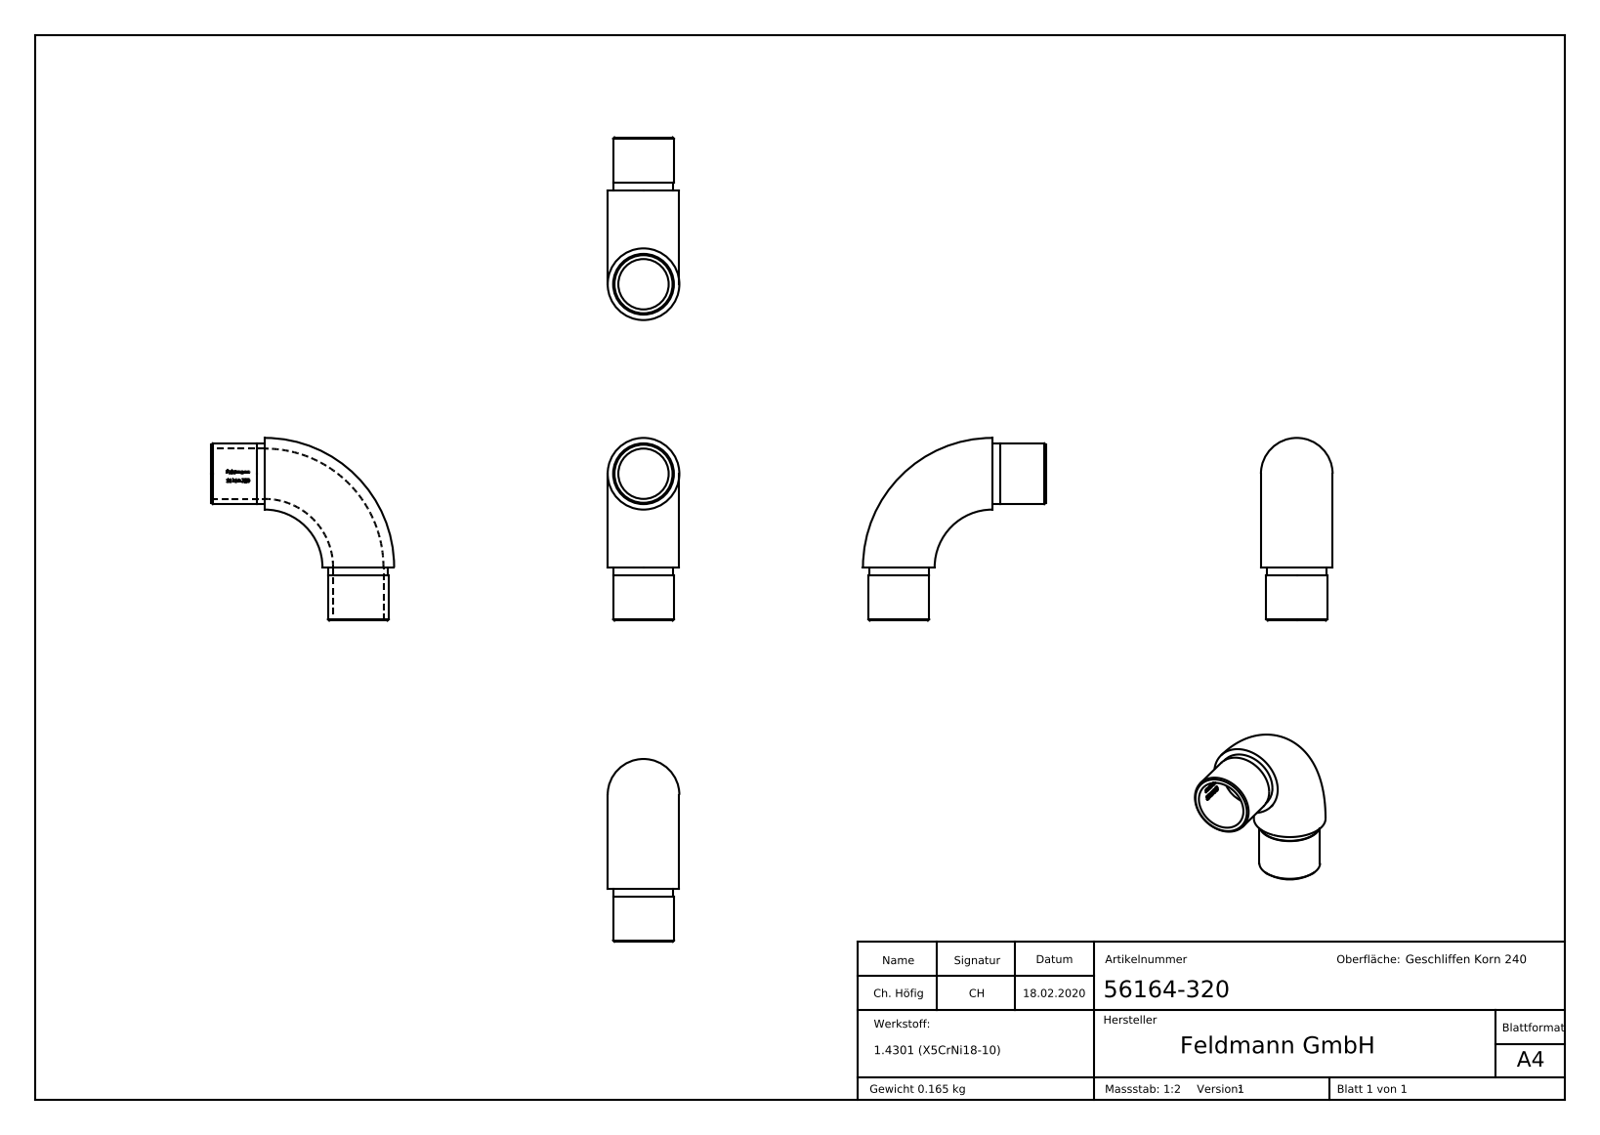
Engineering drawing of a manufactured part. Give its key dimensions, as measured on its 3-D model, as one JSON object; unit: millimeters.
{"part_name": "56164-320", "step_written_by": "SolidWorks 2015 (CONFIG_CONTROL_DESIGN)", "units": "millimeters", "bodies": {"solids": 1, "faces": 241, "planar": 104, "cylindrical": 30, "other": 107}, "overall_size": [68.6, 68.6, 26.9], "volume_mm3": 20895, "surface_area_mm2": 13776, "round_holes": [[18.9, 2]], "round_bosses_or_shafts": [[22.8, 2], [22.4, 2]], "partial_cylinders_radius": [[9.55, 1]], "face_to_face_distances": [20, 17, 3, 1.26, 0.39, 4.65, 0.99, 2.52, 0.87, 1.38]}
